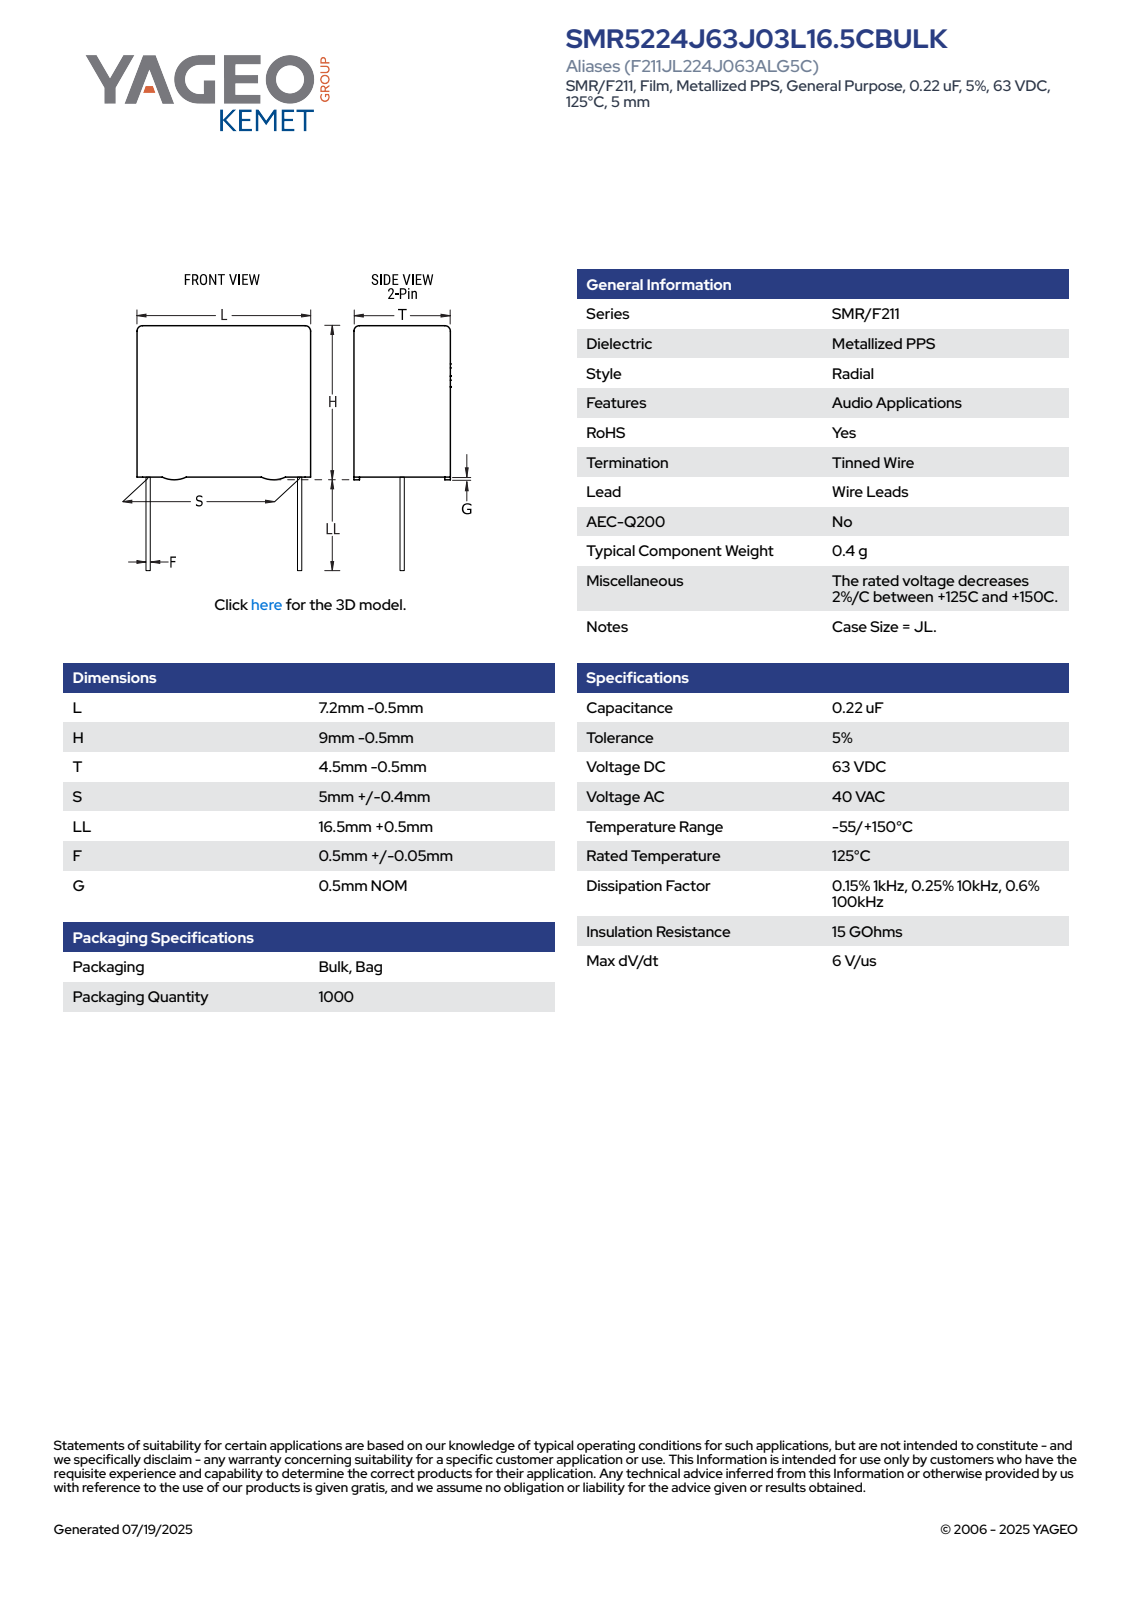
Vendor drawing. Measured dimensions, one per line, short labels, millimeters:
name: CFR_RBG_7.2X9X4.5_L6.7H8.5T4S5LL17F0.55G0.5
written by: SolidWorks 2021 (AUTOMOTIVE_DESIGN)
unit: mm
bodies: 4 solids, 89 faces (81 planar, 8 cylindrical, 0 other)
size: 25.5 × 6.7 × 4
volume: 222 mm³; area: 291 mm²
bosses: 2× ⌀0.55
rounds: 4× R0.5
face distances: 4, 6.7, 8, 3.77, 3.54, 0.5, 8.5, 2.49, 17, 17.5
